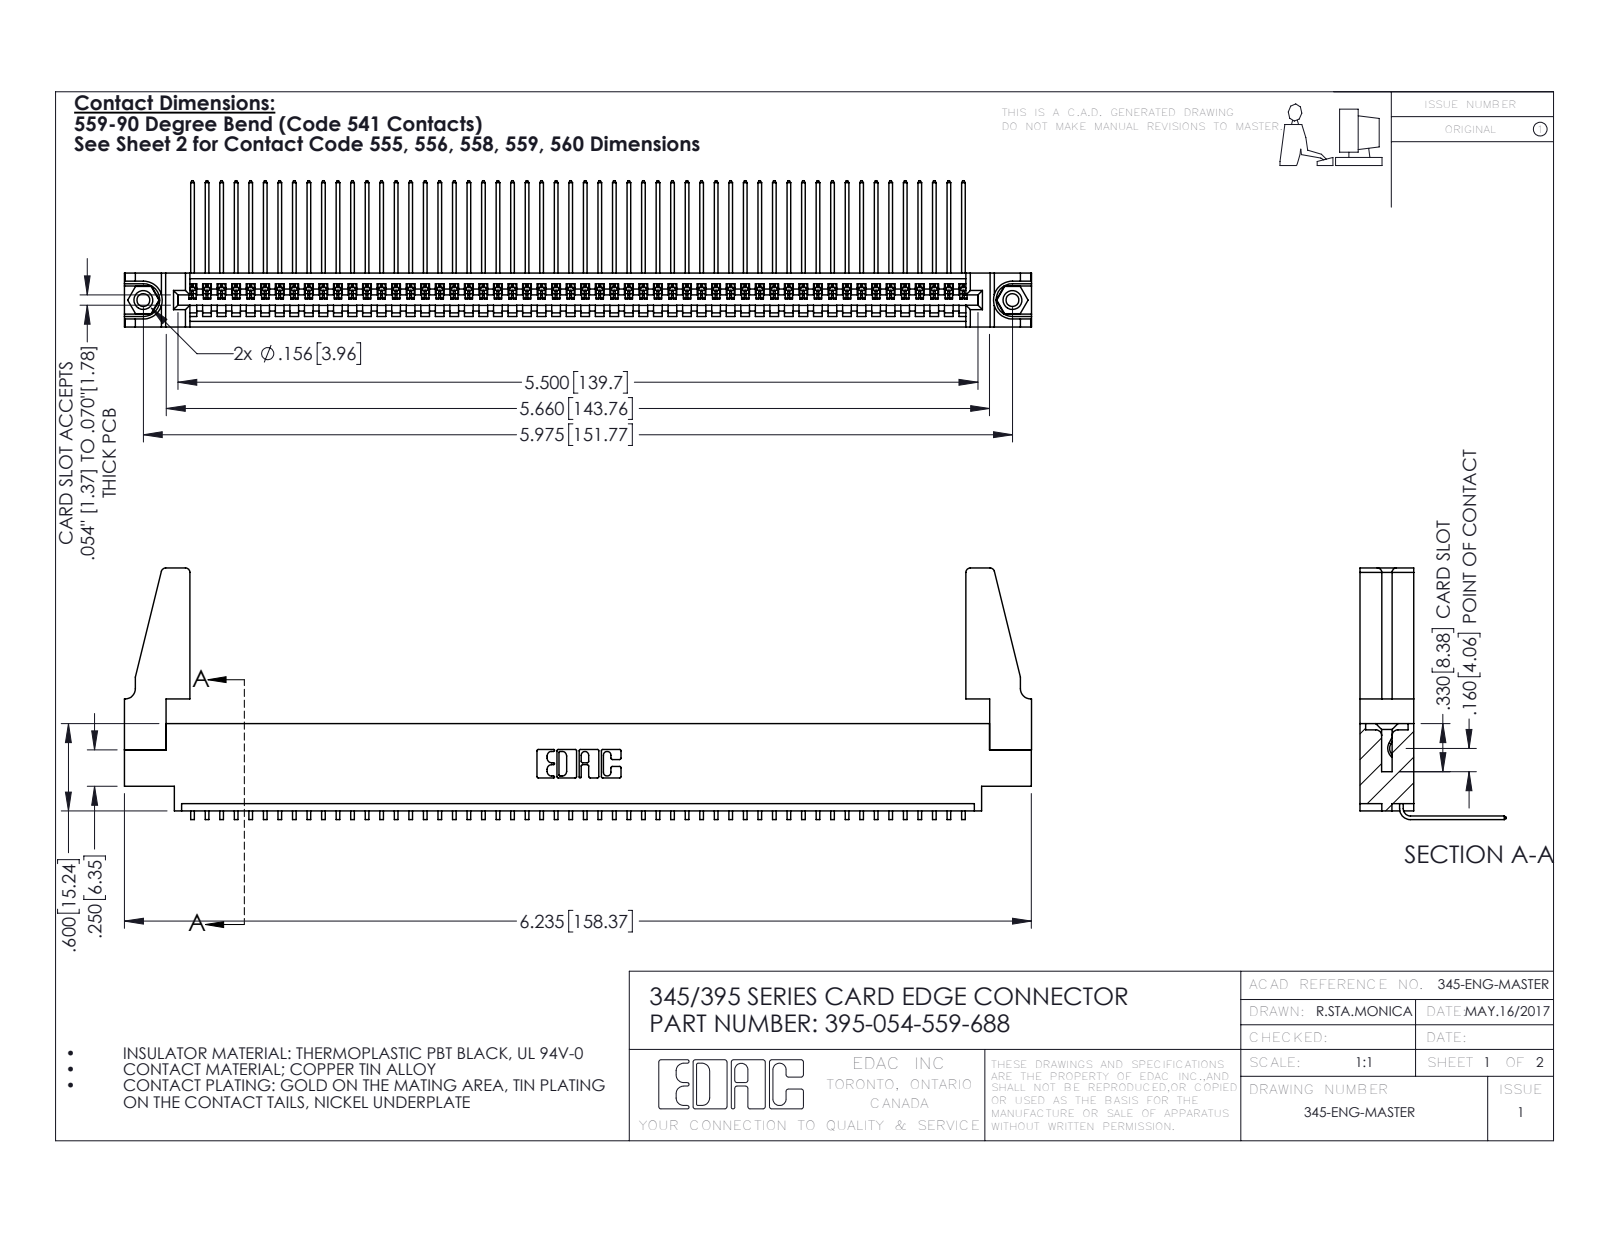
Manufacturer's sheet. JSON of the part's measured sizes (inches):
{"part_name": "345-292-001_558 559 Tail - 1; 345-220-078_345-220-088; 395-054-559-688; 345 Part_0.170 Offset - 0.156 Dia-TH (+1 more)", "step_written_by": "SolidWorks 2016 (CONFIG_CONTROL_DESIGN)", "units": "inches", "bodies": {"solids": 59, "faces": 3494, "planar": 2424, "cylindrical": 1054, "other": 16}, "overall_size": [6.236, 1.729, 1.005], "volume_in3": 1.127, "surface_area_in2": 38.27, "round_holes": [[0.089, 2], [0.125, 2], [0.156, 2], [0.064, 1]], "round_bosses_or_shafts": [[0.155, 2]], "partial_cylinders_radius": [[0.006, 108], [0.01, 22], [0.03, 8], [0.007, 6], [0.031, 6], [0.026, 3], [0.031, 2], [0.04, 2]], "face_to_face_distances": [0.072, 0.37, 0.298, 0.2, 0.098, 0.272, 0.025, 0.225, 0.175, 0.149], "hole_center_spacings": [0.27, 5.739, 5.975]}
